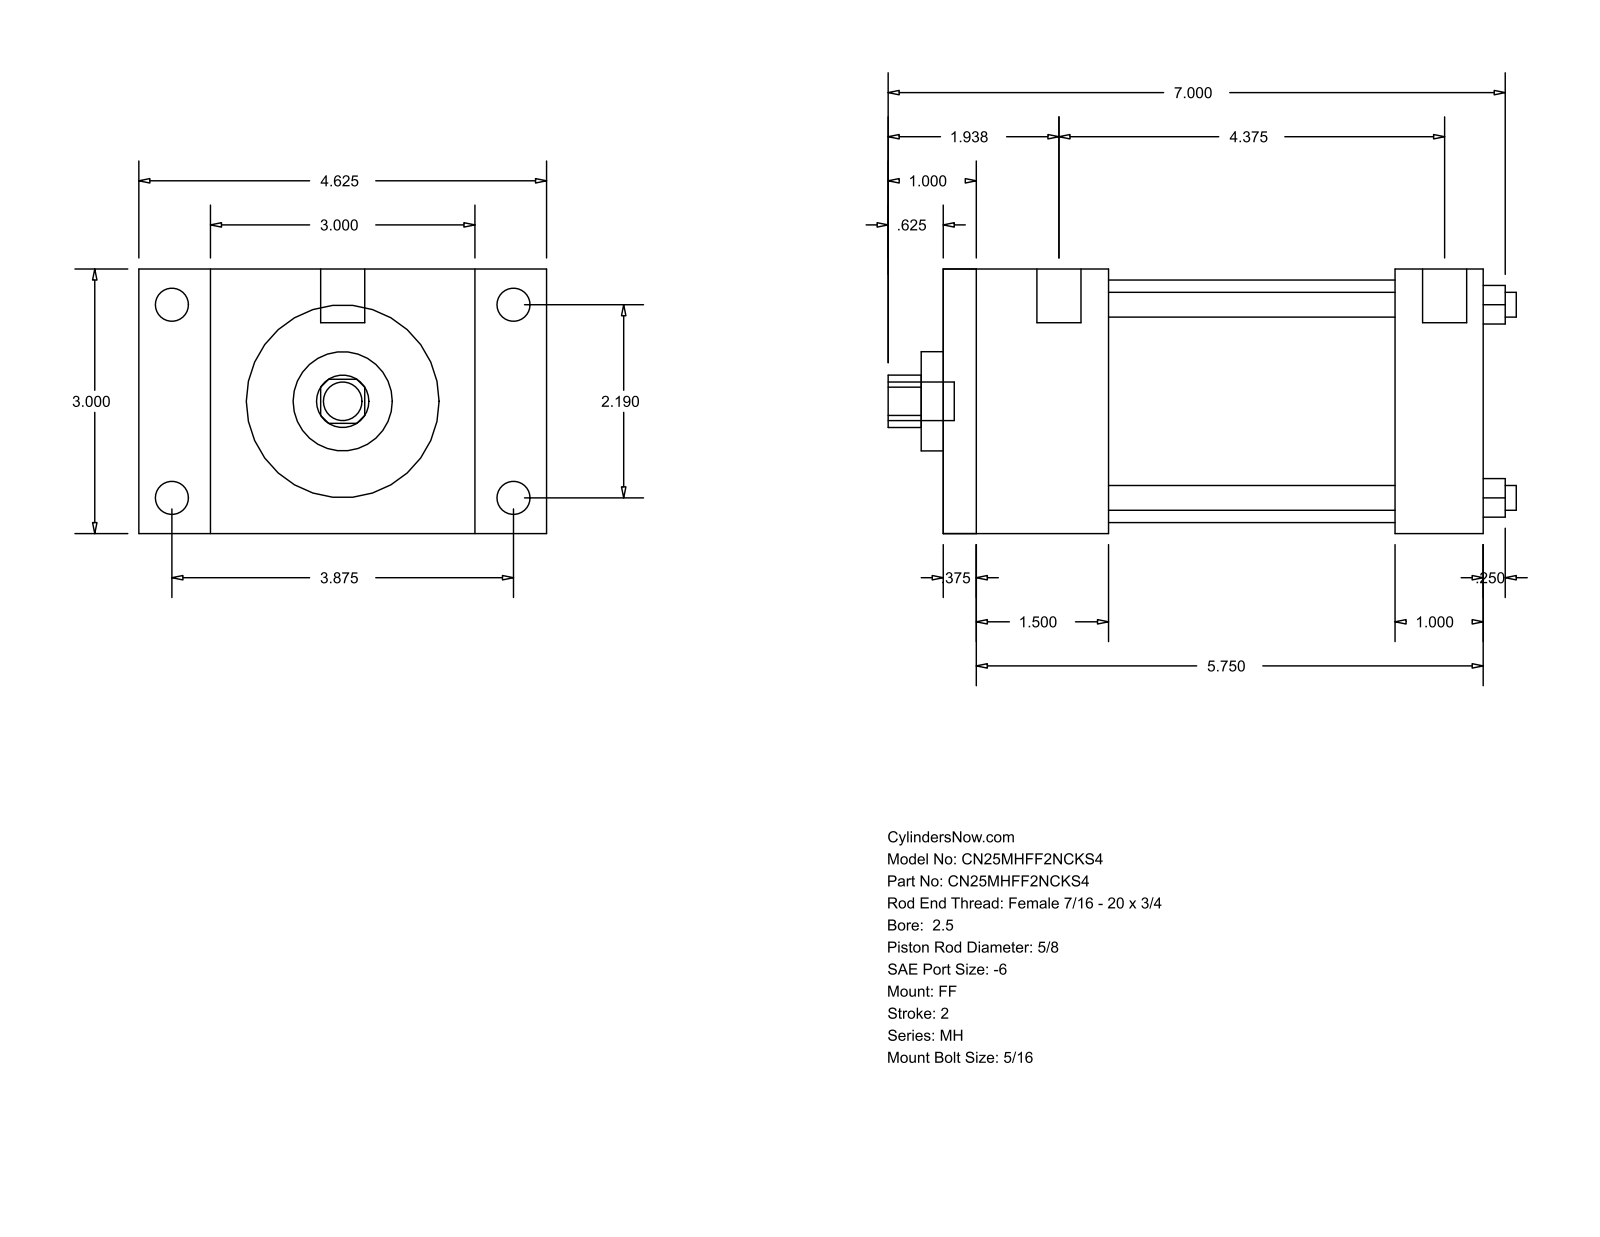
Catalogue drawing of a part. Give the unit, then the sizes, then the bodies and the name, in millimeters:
Units: millimetres
Overall size (bounding box): 180.97 × 117.47 × 76.2
Round holes (diameter × count): ⌀7.14 ×4, ⌀15.88 ×1, ⌀28.57 ×1, ⌀69.85 ×1
Round bosses / shafts (diameter × count): ⌀9.53 ×4, ⌀5.56 ×4, ⌀12.7 ×2, ⌀11.11 ×1
Partial cylindrical surfaces — rounded edges, fillets, slot ends (radius × count): R7.54 ×1
Main face-to-face distances: 76.2, 155.57, 9.52, 146.05, 25.4, 47.62, 130.17, 38.1, 120.65, 82.55
Hole centre spacings: 39.33, 55.62, 78.66
Bodies: 0 solids, 92 faces (64 planar, 28 cylindrical, 0 other)
Part name (STEP PRODUCT): MH_FF__0250_0.625
STEP written by: GSSL Pune (CONFIG_CONTROL_DESIGN)
